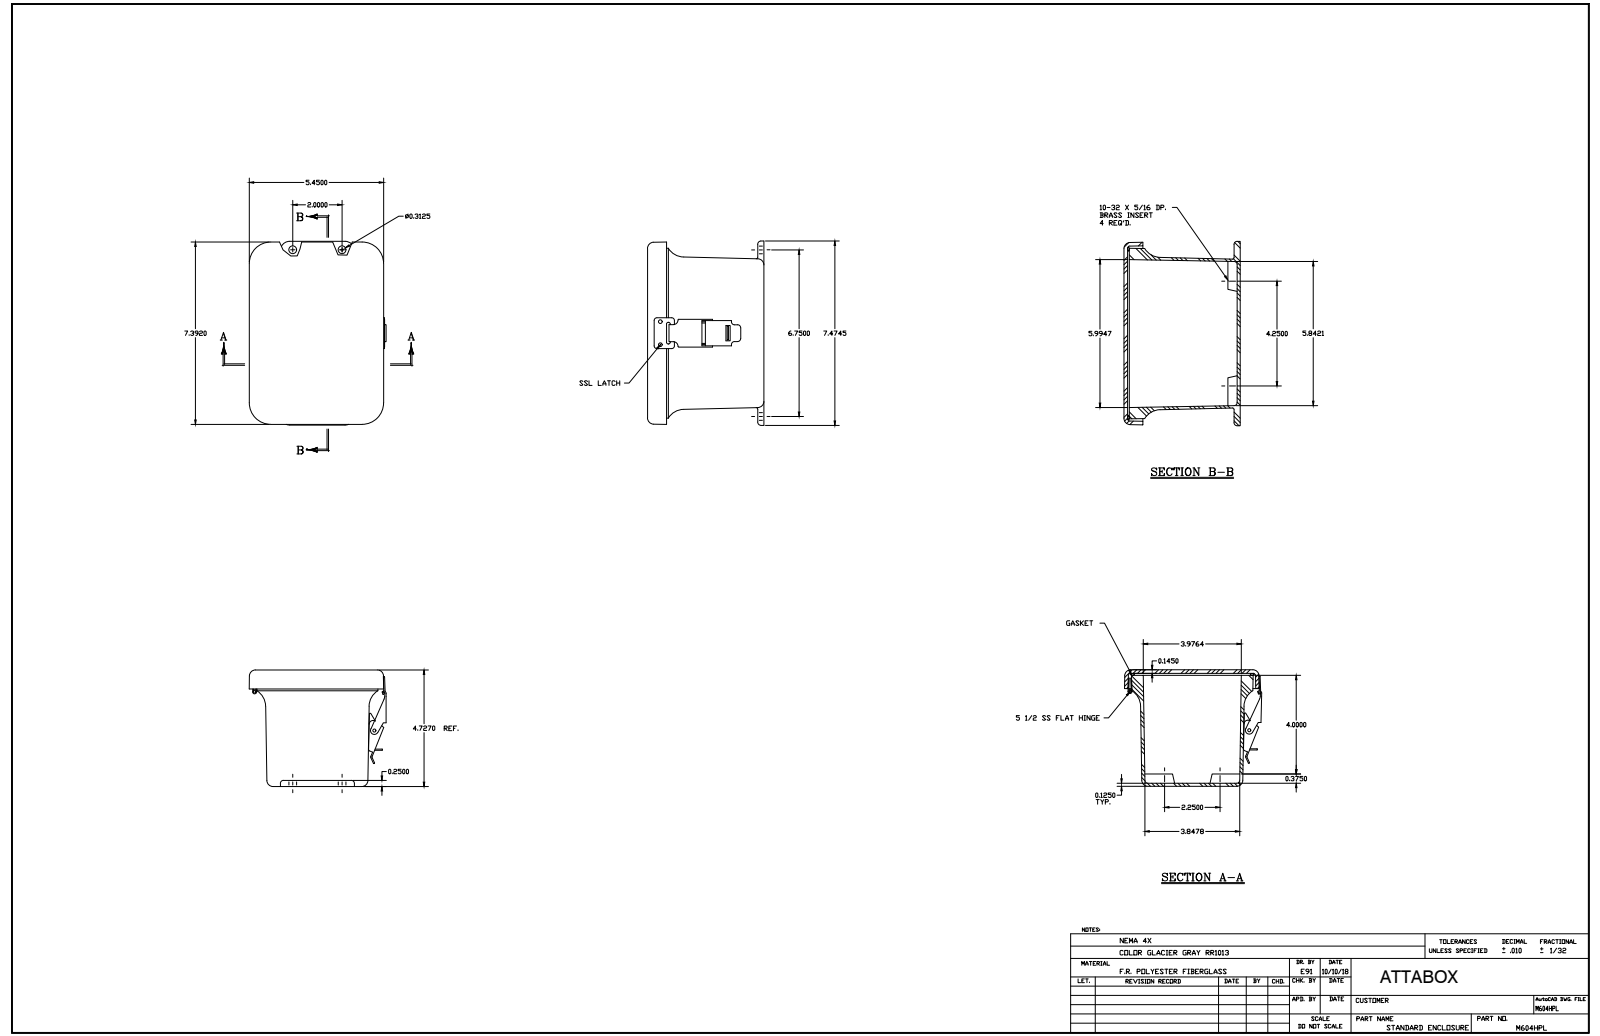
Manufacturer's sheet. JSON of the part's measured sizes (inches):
{"part_name": "M604HPL", "step_written_by": "SolidWorks 2018 (AUTOMOTIVE_DESIGN)", "units": "inches", "bodies": {"solids": 25, "faces": 627, "planar": 249, "cylindrical": 254, "other": 124}, "overall_size": [7.474, 5.617, 4.717], "volume_in3": 31.61, "surface_area_in2": 407.8, "round_holes": [[0.14, 11], [0.131, 5], [0.152, 5], [0.104, 4], [0.156, 4], [0.218, 4], [0.13, 2], [0.135, 2], [0.135, 2], [0.085, 1], [0.085, 1], [0.375, 1]], "round_bosses_or_shafts": [[0.125, 7], [0.25, 5], [0.27, 4], [0.125, 2], [0.3, 1], [0.17, 1], [0.155, 1], [0.12, 1]], "partial_cylinders_radius": [[0.031, 20], [0.125, 16], [0.015, 12], [0.045, 8], [0.25, 8], [0.03, 6], [0.2, 5], [0.022, 4]], "face_to_face_distances": [0.145, 4.572, 4.717, 0.125, 4.447, 4.592, 4.5, 4.375, 0.072, 0.217], "hole_center_spacings": [0.937, 2.5, 3.339, 0.75, 0.469, 0.5, 1.341, 1.467]}
